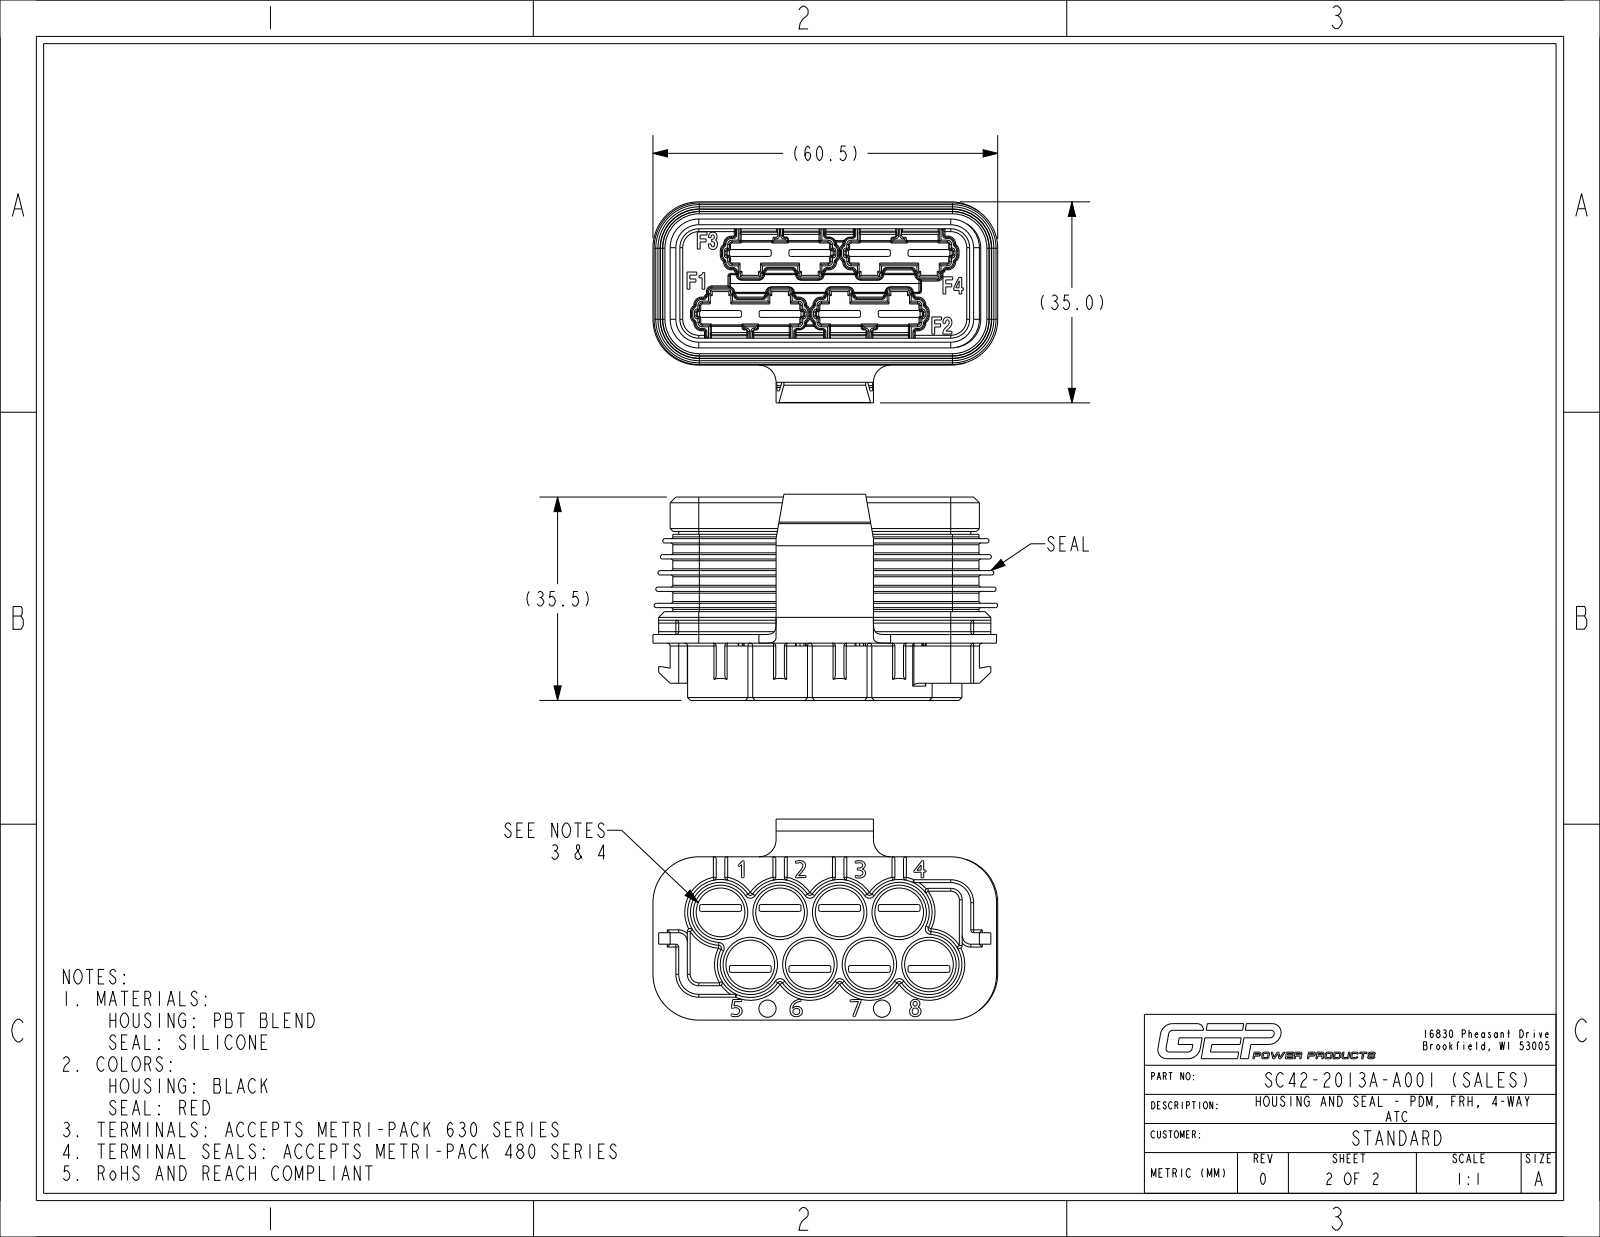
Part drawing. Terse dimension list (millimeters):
name: PC26-2007A-B001_NCF_SALES; C14-1011_INSTALLED; PC42-2013A-A001_NCF_SALES_ASM; SC42-2013A-A001_NCF_ASM
written by: CREO PARAMETRIC BY PTC INC, 2017110 (CONFIG_CONTROL_DESIGN)
unit: mm
bodies: 2 solids, 2597 faces (864 planar, 805 cylindrical, 928 other)
size: 60.2 × 36 × 35.09
volume: 25 783 mm³; area: 28 485 mm²
holes: 8× ⌀8.5
bosses: 2× ⌀3
rounds: 202× R0.2, 82× R0.5, 80× R0.35, 40× R0.31, 34× R0.3, 32× R0.24, 32× R1.15, 22× R0.25
face distances: 1.5, 0.76, 5.03, 3.83, 14.47, 15.67, 1.2, 10.64, 4, 5.5
hole spacings: 10.48, 10.4, 18.06, 20.8, 27.55, 31.2, 37.52
